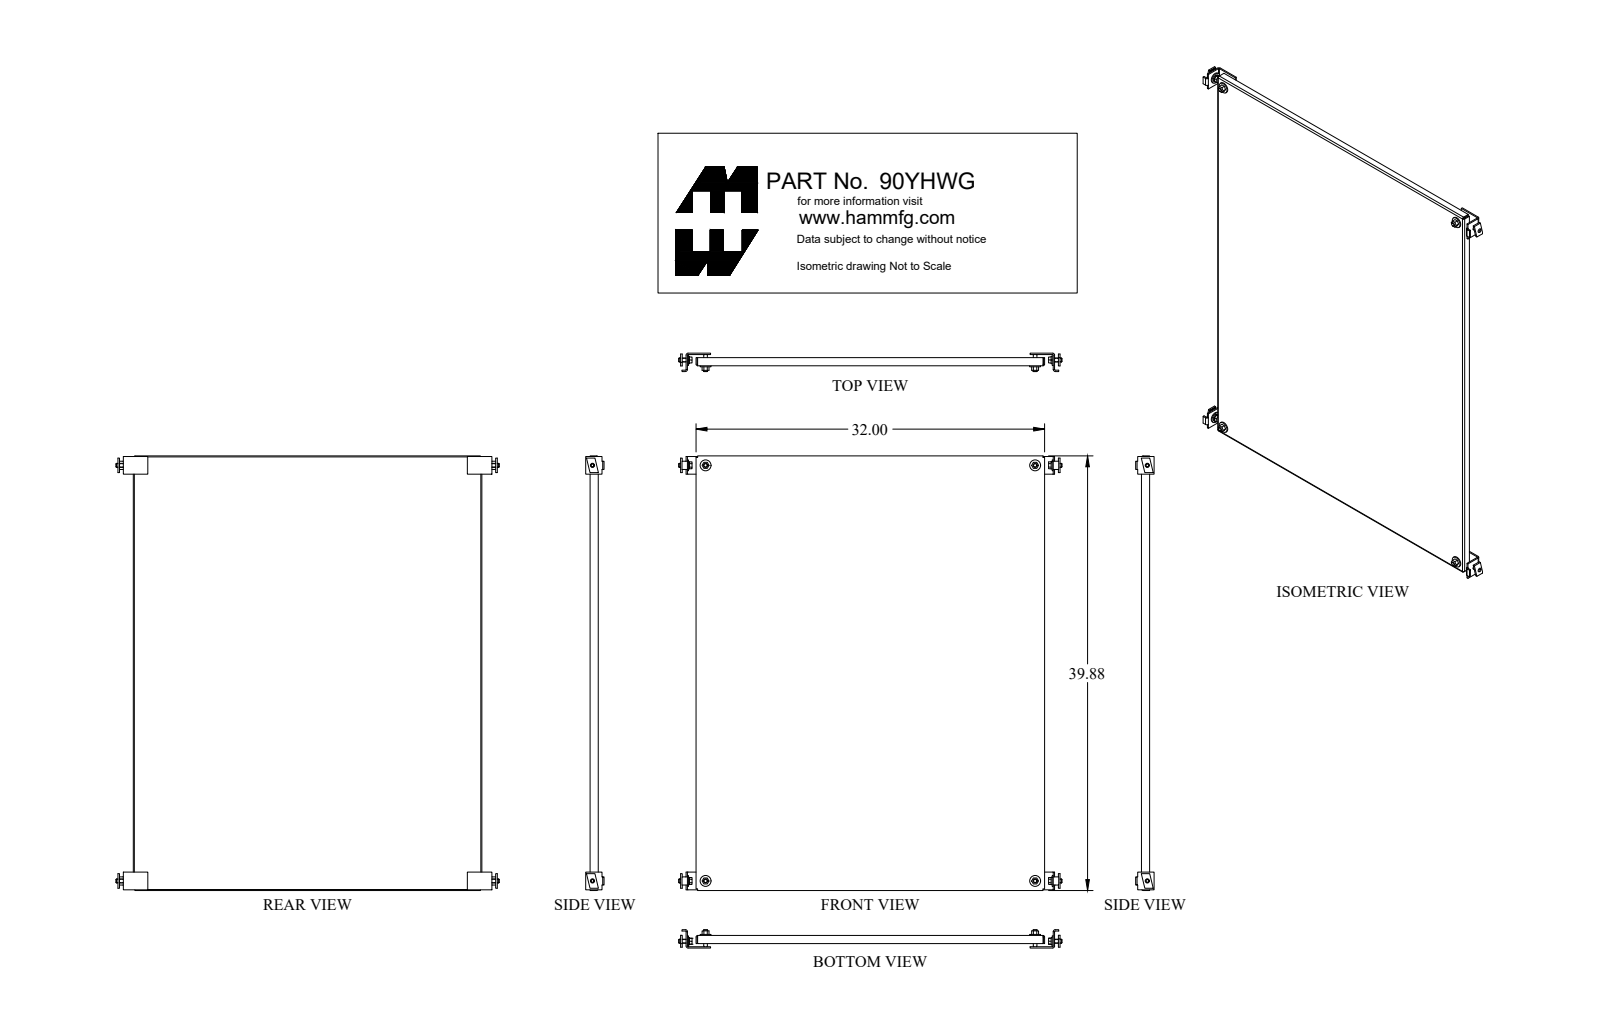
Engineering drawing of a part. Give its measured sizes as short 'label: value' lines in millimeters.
name: 90YHWG_Default
written by: SolidWorks 2018 (CONFIG_CONTROL_DESIGN)
unit: mm
bodies: 9 solids, 190 faces (94 planar, 64 cylindrical, 32 other)
size: 1012.8 × 878.4 × 42.8
volume: 2 181 000 mm³; area: 1 809 000 mm²
holes: 4× ⌀14.3, 2× ⌀11.1
bosses: 4× ⌀16.5, 4× ⌀9.5, 4× ⌀8.4
rounds: 4× R1.2, 4× R1.5, 4× R3.6, 4× R4.7
face distances: 2.4, 810.4, 1010.4, 812.8, 808, 3.2, 1012.8, 1008, 26.2, 23.8
hole spacings: 768.4, 968.4, 1236.2, 968.5
